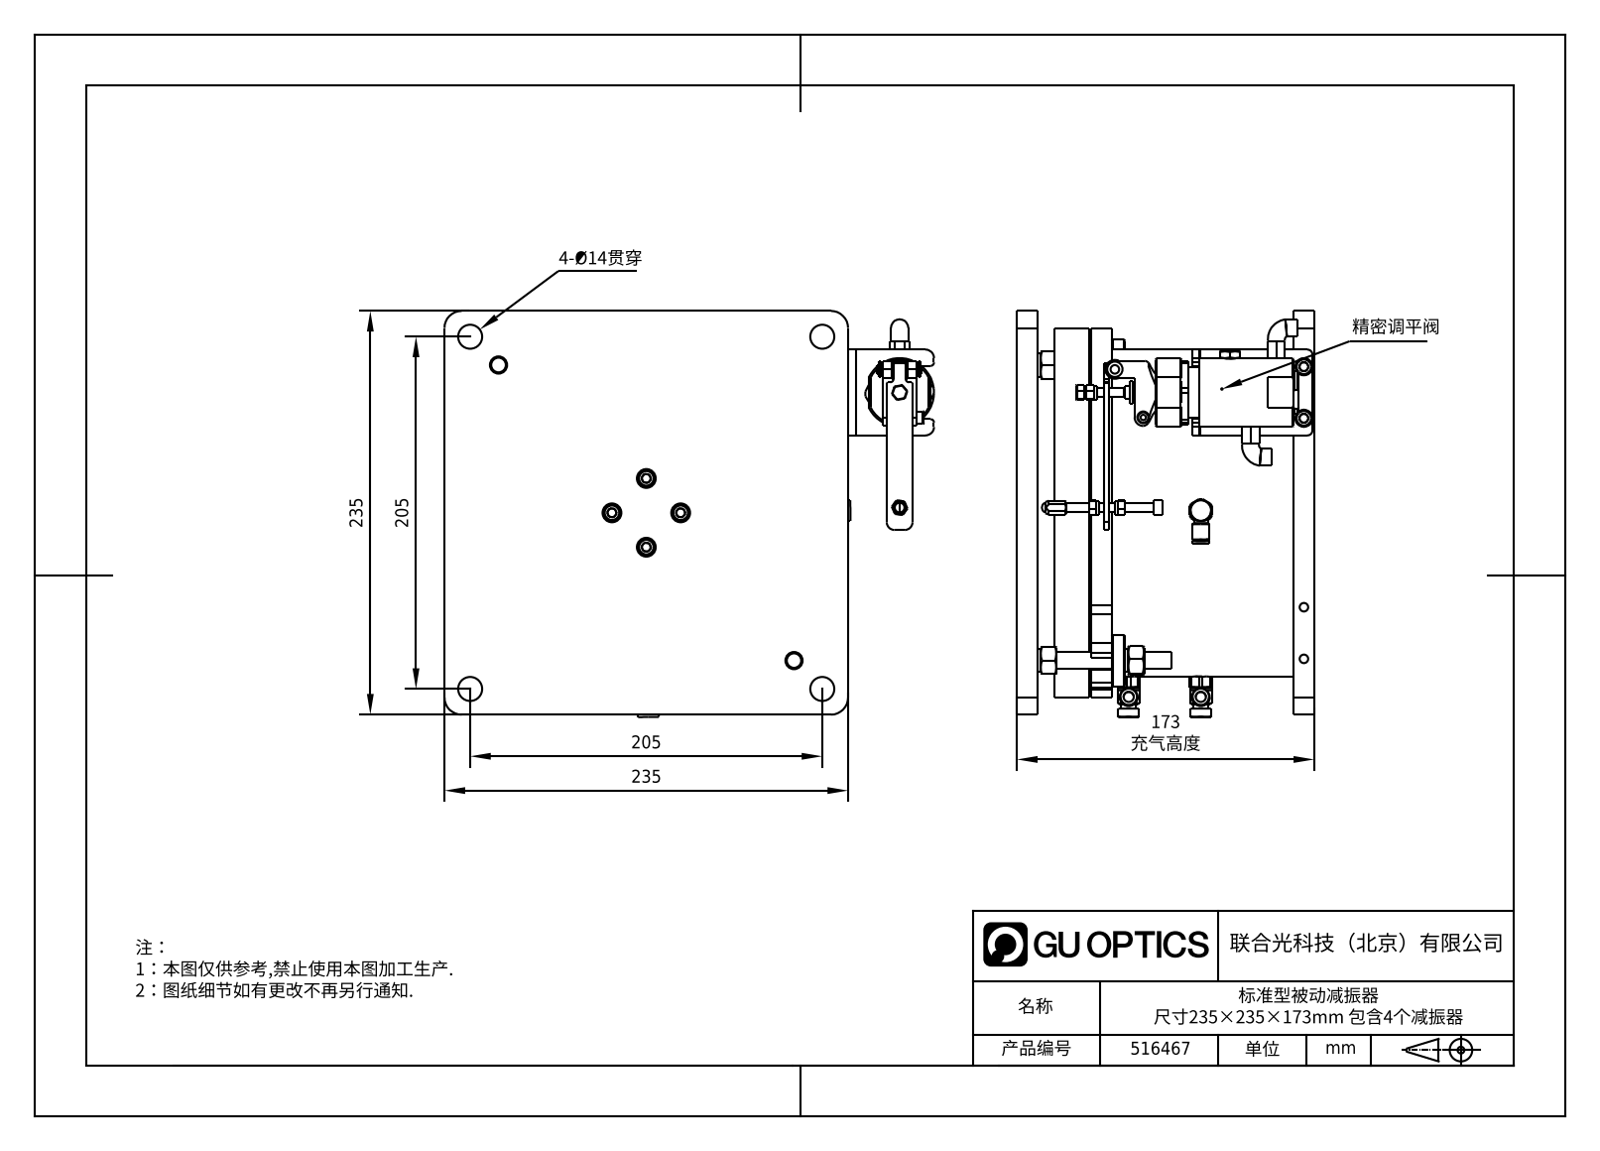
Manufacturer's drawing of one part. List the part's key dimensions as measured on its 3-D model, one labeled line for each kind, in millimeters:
Part name (STEP PRODUCT): 516467
STEP written by: SolidWorks 2020 (CONFIG_CONTROL_DESIGN)
Units: millimetres
Bodies: 0 solids, 494 faces (280 planar, 147 cylindrical, 67 other)
Overall size (bounding box): 285 × 236.41 × 173
Round holes (diameter × count): ⌀14 ×4, ⌀5 ×3, ⌀9.7 ×3, ⌀12 ×2, ⌀9 ×1, ⌀11 ×1, ⌀11.5 ×1, ⌀12.7 ×1, ⌀13 ×1, ⌀40 ×1, ⌀215 ×1
Round bosses / shafts (diameter × count): ⌀10 ×6, ⌀11 ×4, ⌀30 ×3, ⌀12.6 ×3, ⌀12 ×3, ⌀10.4 ×3, ⌀8.45 ×3, ⌀8.1 ×3
Partial cylindrical surfaces — rounded edges, fillets, slot ends (radius × count): R5 ×14, R10 ×6, R0.3 ×4, R2 ×4, R7 ×3, R3 ×2, R4.5 ×2, R0.74 ×1
Main face-to-face distances: 12, 161, 149, 173, 43, 118, 55, 106, 130, 31
Hole centre spacings: 144.96, 189.22, 205, 23.33, 121.62, 266.58, 289.91, 30
